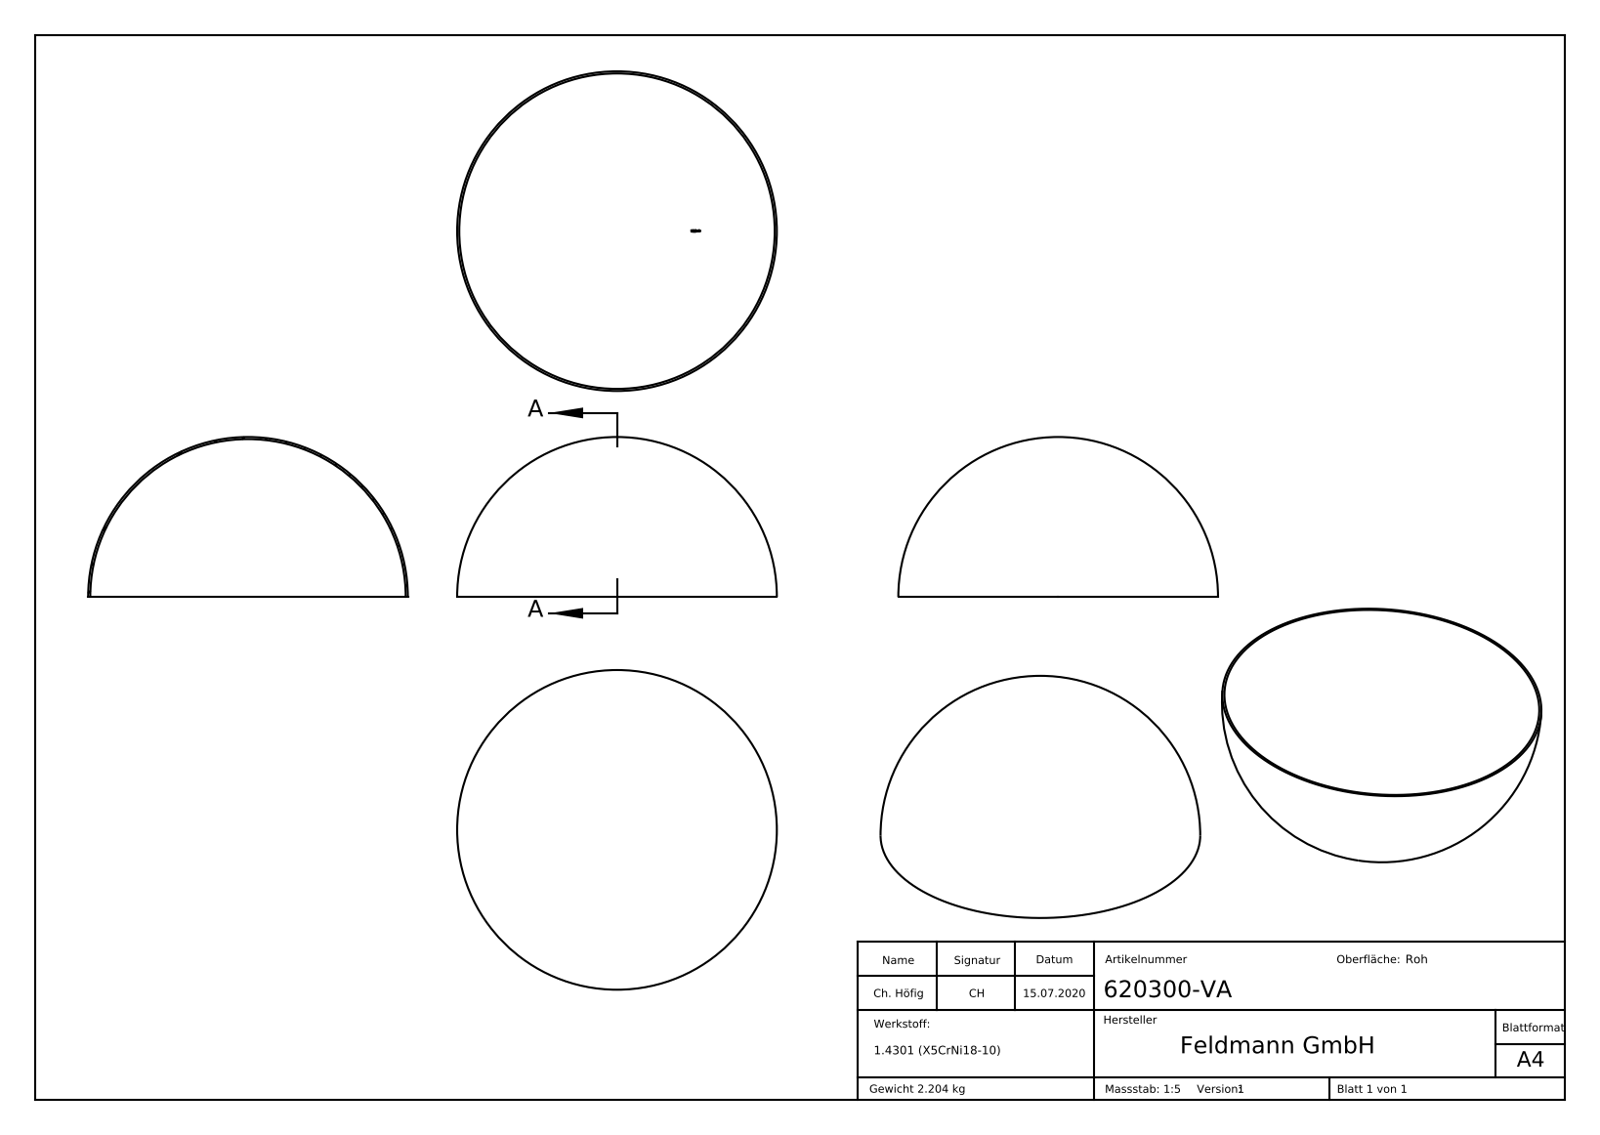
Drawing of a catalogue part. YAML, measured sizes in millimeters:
part_name: "620300-VA"
step_written_by: "SolidWorks 2018 (CONFIG_CONTROL_DESIGN)"
units: millimeters
bodies: {solids: 1, faces: 220, planar: 89, cylindrical: 0, other: 131}
overall_size: [300, 300, 150]
volume: 278990
surface_area: 280875
face_to_face_distances: [0.45, 0.5, 0.61, 1.19, 0.53, 0.55, 0.81, 1.31, 0.85, 0.31]
